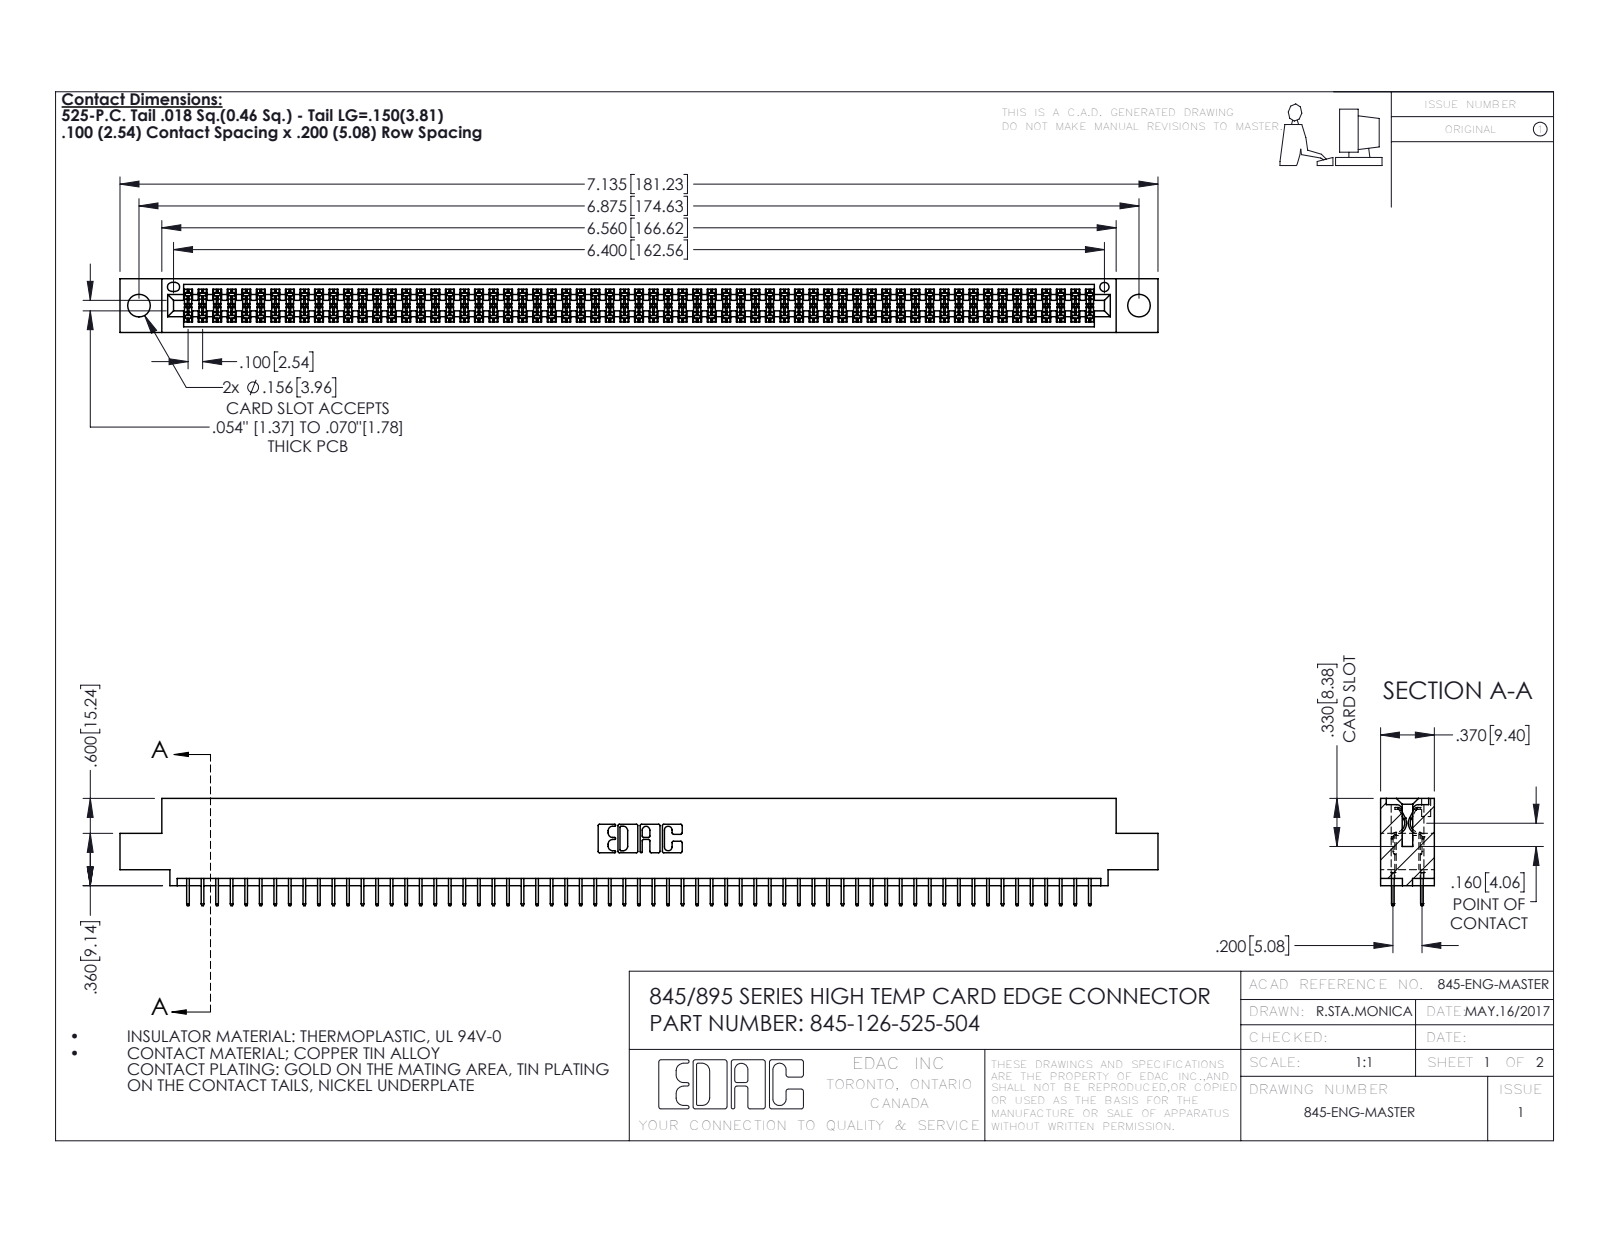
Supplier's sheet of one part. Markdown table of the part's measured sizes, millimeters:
| quantity | value |
| --- | --- |
| part name | 845-126-525-504; 845 Part_0.110 Offset - 0.156 Dia-TH; 345-292-001_345-293-125 |
| STEP written by | SolidWorks 2020 (CONFIG_CONTROL_DESIGN) |
| units | millimeters |
| bodies | 127 solids, 6934 faces (4998 planar, 1936 cylindrical, 0 other) |
| overall size | 181.2 × 18.7 × 9.4 |
| volume | 17 440 mm³ |
| surface area | 25 460 mm² |
| round holes (diameter × count) | 4 × 2, 1.6 × 1 |
| partial cylindrical surfaces (radius × count) | 0.2 × 189, 0.3 × 22, 0.2 × 6, 0.8 × 6, 0.7 × 3, 0.4 × 2, 0.5 × 2, 0.6 × 2 |
| main face-to-face distances | 1.8, 7.6, 5.1, 9.4, 2.5, 6.9, 0.6, 5.7, 1.8, 4.4 |
| hole center spacings | 6.9, 168.6, 174.6 |
